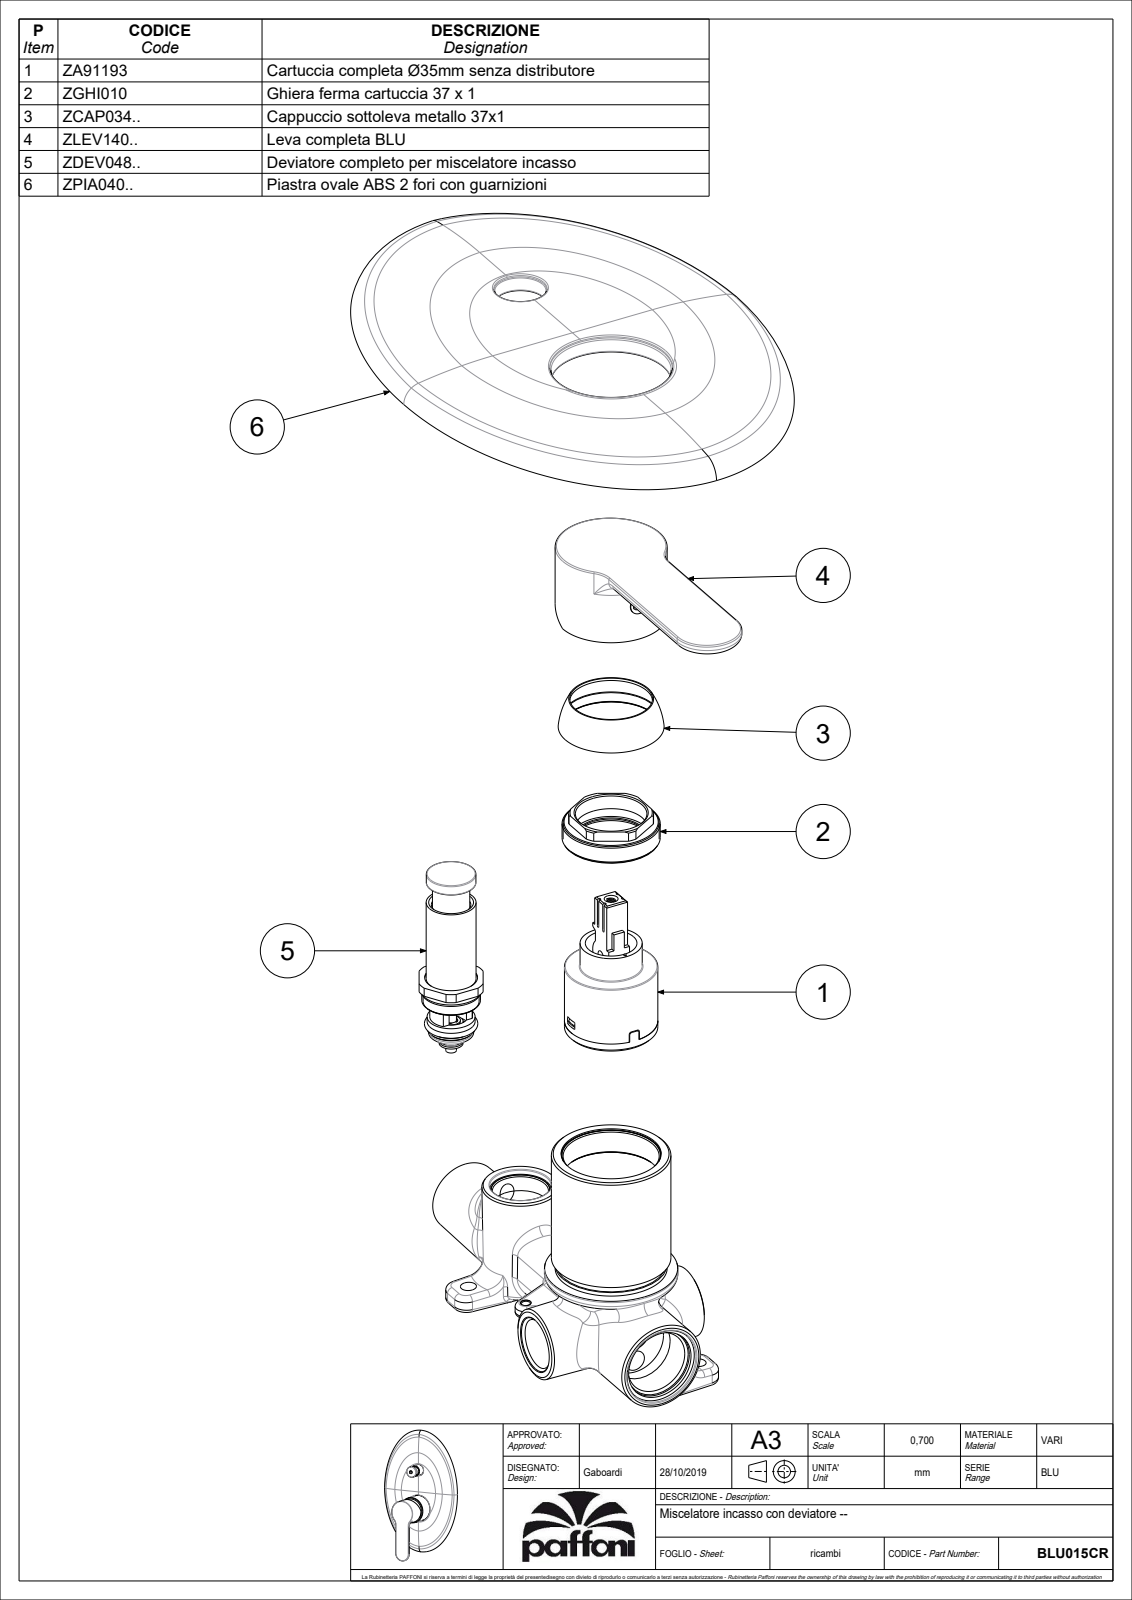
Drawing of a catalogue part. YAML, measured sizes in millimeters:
part_name: "BLU015CR"
step_written_by: "CREO PARAMETRIC BY PTC INC, 2020044 (CONFIG_CONTROL_DESIGN)"
units: millimeters
bodies: {solids: 5, faces: 848, planar: 353, cylindrical: 263, other: 232}
overall_size: [222, 146, 67.55]
volume: 124947
surface_area: 100171
round_holes:
  - {diameter: 7, count: 3}
  - {diameter: 12, count: 3}
  - {diameter: 2, count: 2}
  - {diameter: 3.3, count: 2}
  - {diameter: 5, count: 2}
  - {diameter: 8, count: 2}
  - {diameter: 20, count: 2}
  - {diameter: 3, count: 1}
  - {diameter: 3.4, count: 1}
  - {diameter: 4, count: 1}
  - {diameter: 4.5, count: 1}
  - {diameter: 4.6, count: 1}
round_bosses_or_shafts:
  - {diameter: 4.8, count: 2}
  - {diameter: 4, count: 2}
  - {diameter: 51, count: 1}
  - {diameter: 49, count: 1}
  - {diameter: 44.8, count: 1}
  - {diameter: 42, count: 1}
  - {diameter: 39, count: 1}
  - {diameter: 35, count: 1}
partial_cylinders:
  - {radius: 0.5, count: 41}
  - {radius: 0.3, count: 19}
  - {radius: 1.2, count: 10}
  - {radius: 1, count: 9}
  - {radius: 4.5, count: 3}
  - {radius: 1.6, count: 2}
  - {radius: 2.5, count: 2}
  - {radius: 10, count: 2}
face_to_face_distances: [62.8, 3, 1, 59.8, 63.8, 60.8, 26.2, 23, 4.8, 3.45]
hole_center_spacings: [0.71, 8.51, 8.6, 9.85, 10.42, 12, 12.14, 13.04]
